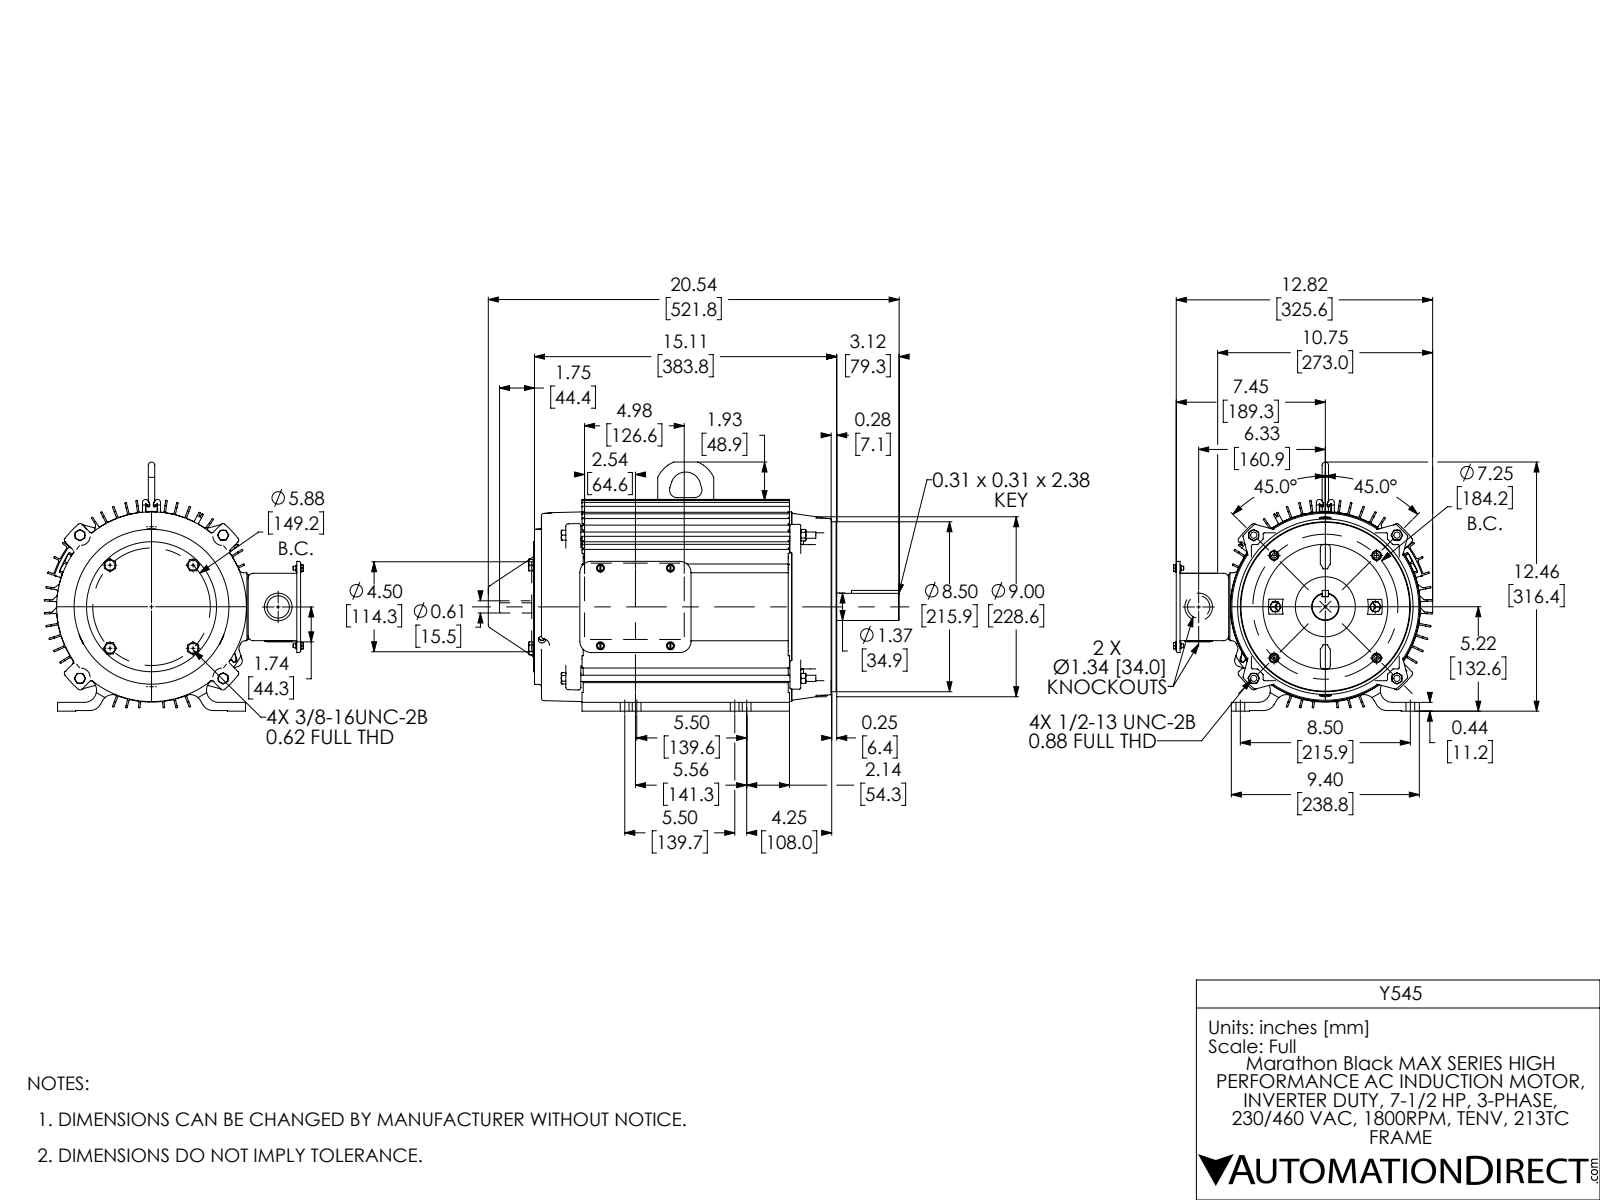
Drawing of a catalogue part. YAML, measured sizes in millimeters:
part_name: "Y545"
step_written_by: "SolidWorks 2017 (AUTOMOTIVE_DESIGN)"
units: millimeters
bodies: {solids: 31, faces: 3696, planar: 999, cylindrical: 1022, other: 1675}
overall_size: [521.8, 329.1, 316.4]
volume: 4102000
surface_area: 1577000
round_holes:
  - {diameter: 11.1, count: 8}
  - {diameter: 8.7, count: 6}
  - {diameter: 4.4, count: 4}
  - {diameter: 5.6, count: 4}
  - {diameter: 6.5, count: 4}
  - {diameter: 7.9, count: 4}
  - {diameter: 7.9, count: 4}
  - {diameter: 10.3, count: 4}
  - {diameter: 10.7, count: 4}
  - {diameter: 4.4, count: 3}
  - {diameter: 6.4, count: 2}
  - {diameter: 8.4, count: 2}
round_bosses_or_shafts:
  - {diameter: 7.9, count: 6}
  - {diameter: 12.7, count: 4}
  - {diameter: 10.1, count: 4}
  - {diameter: 9.5, count: 4}
  - {diameter: 7.5, count: 4}
  - {diameter: 4.8, count: 4}
  - {diameter: 11.2, count: 2}
  - {diameter: 235.5, count: 1}
partial_cylinders:
  - {radius: 1.5, count: 162}
  - {radius: 3, count: 130}
  - {radius: 1, count: 32}
  - {radius: 6.4, count: 25}
  - {radius: 0.8, count: 19}
  - {radius: 4.8, count: 12}
  - {radius: 2.4, count: 8}
  - {radius: 6.4, count: 8}
face_to_face_distances: [1.9, 1.5, 66.6, 69.4, 2.5, 383.8, 68.1, 65, 6.4, 0.8]
hole_center_spacings: [118.5, 148.7, 158.2, 53.8, 101.6, 15.2, 17.5, 36.5]
